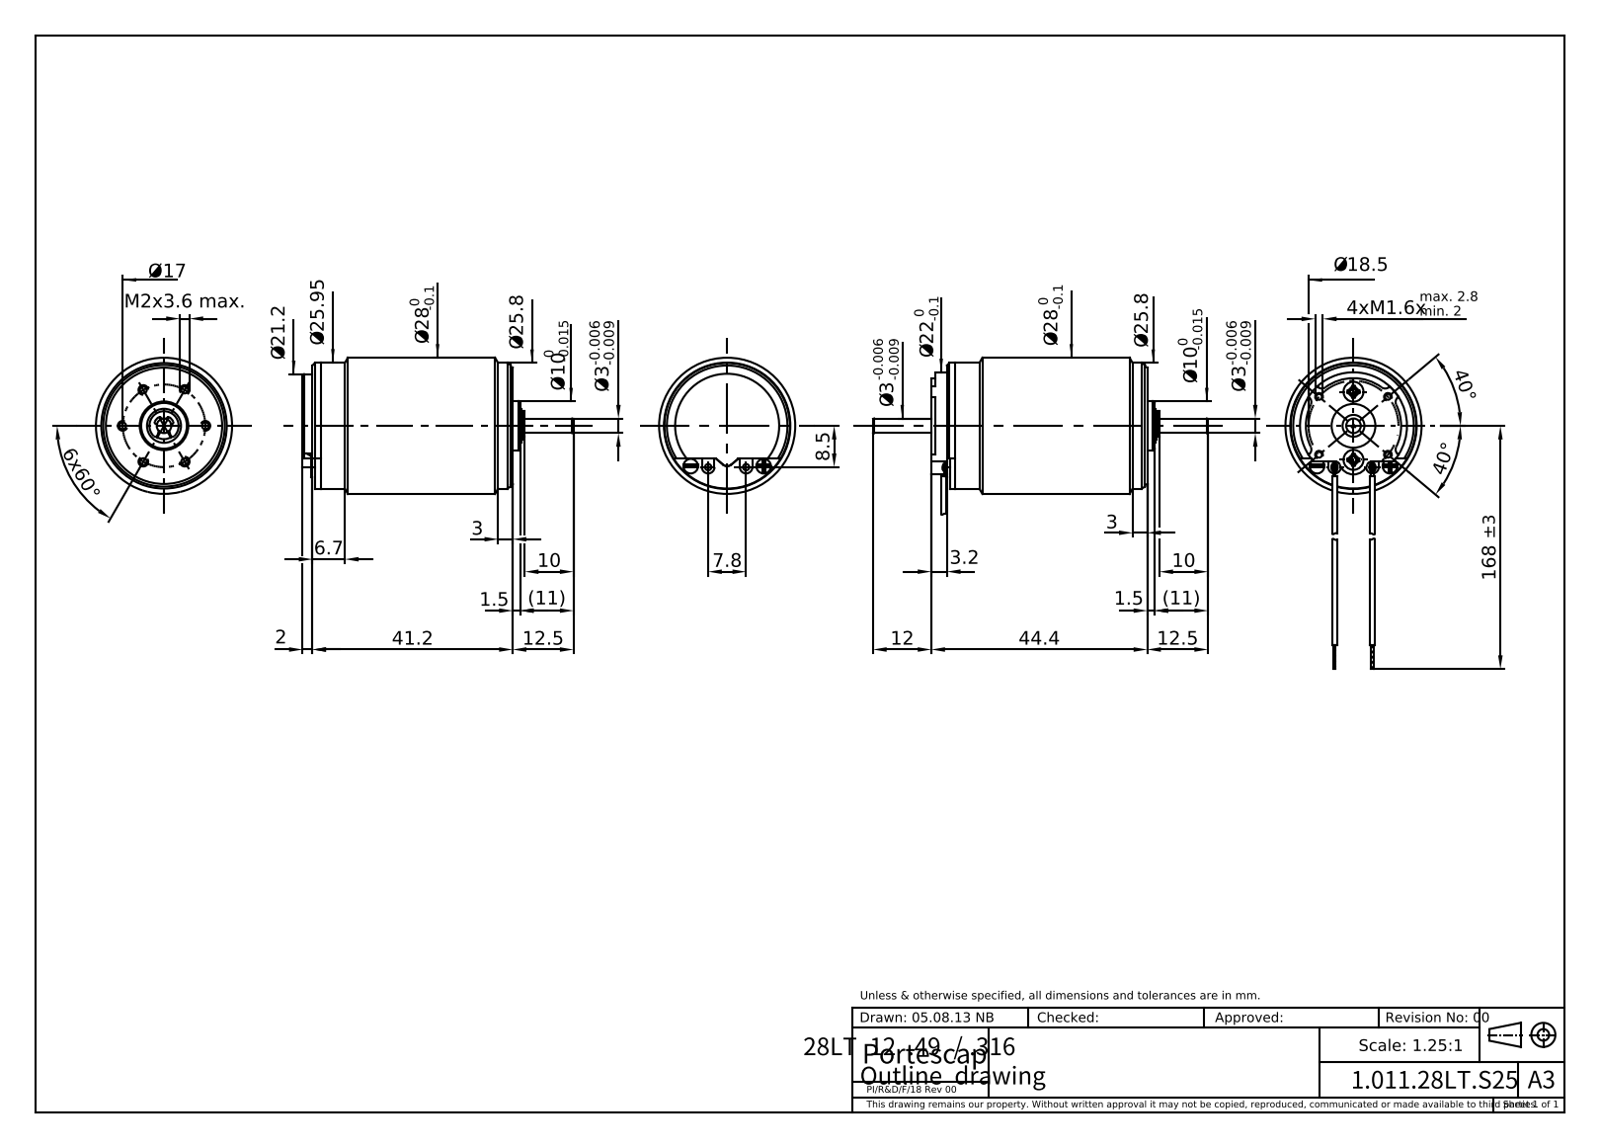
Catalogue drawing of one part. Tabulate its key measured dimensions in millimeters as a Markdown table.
| quantity | value |
| --- | --- |
| part name | PRT0007 |
| STEP written by | PRO/ENGINEER BY PARAMETRIC TECHNOLOGY CORPORATION, 2014310 (CONFIG_CONTROL_DESIGN) |
| units | millimeters |
| bodies | 1 solid, 164 faces (59 planar, 85 cylindrical, 20 other) |
| overall size | 55.71 × 28 × 28 |
| volume | 25 021 mm³ |
| surface area | 6 513 mm² |
| round holes (diameter × count) | 1.6 × 6, 2 × 6, 1.5 × 4, 1.8 × 3, 24.7 × 1, 25.3 × 1 |
| round bosses / shafts (diameter × count) | 28 × 1, 25.95 × 1, 25.8 × 1, 25.4 × 1, 24.5 × 1, 10 × 1, 5.5 × 1, 3 × 1 |
| partial cylindrical surfaces (radius × count) | 0.3 × 4, 1.5 × 4, 0.5 × 2, 2.08 × 1, 3 × 1, 10.6 × 1 |
| main face-to-face distances | 39.51, 39.31, 3.7, 3.9, 43.21, 1.9, 41.21, 0.6, 2, 1.7 |
| hole center spacings | 8.5, 14.72, 17.44, 17, 2.4, 3.73, 3.9, 5.48 |
